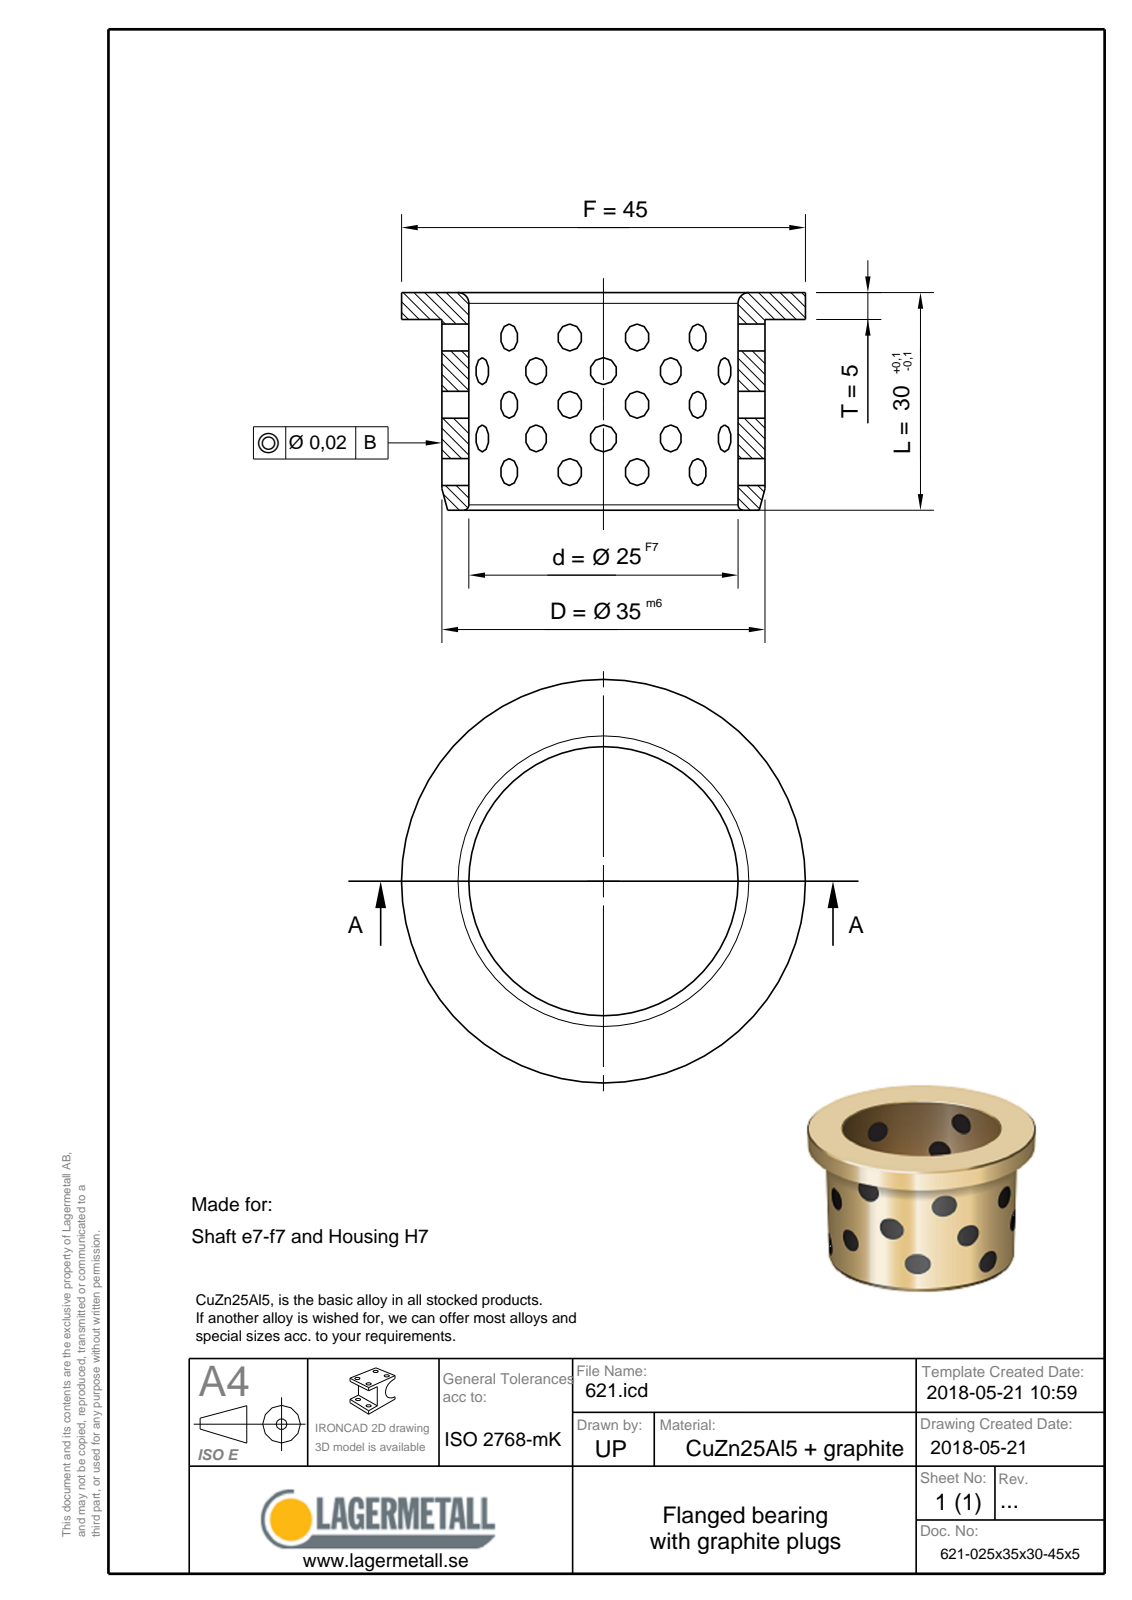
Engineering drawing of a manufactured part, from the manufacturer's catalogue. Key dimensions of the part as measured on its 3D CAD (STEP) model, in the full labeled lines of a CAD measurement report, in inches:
Part name (STEP PRODUCT): 621-025x35x30-45x5
STEP written by: Spatial InterOp 3D (CONFIG_CONTROL_DESIGN)
Units: inches
Bodies: 1 solid, 9 faces (3 planar, 3 cylindrical, 3 other)
Overall size (bounding box): 1.772 × 1.772 × 1.181
Volume: 1.044 in³ · Surface area: 12.11 in²
Round holes (diameter × count): ⌀0.984 ×1
Round bosses / shafts (diameter × count): ⌀1.772 ×1, ⌀1.378 ×1
Main face-to-face distances: 0.197, 0.984, 1.181
